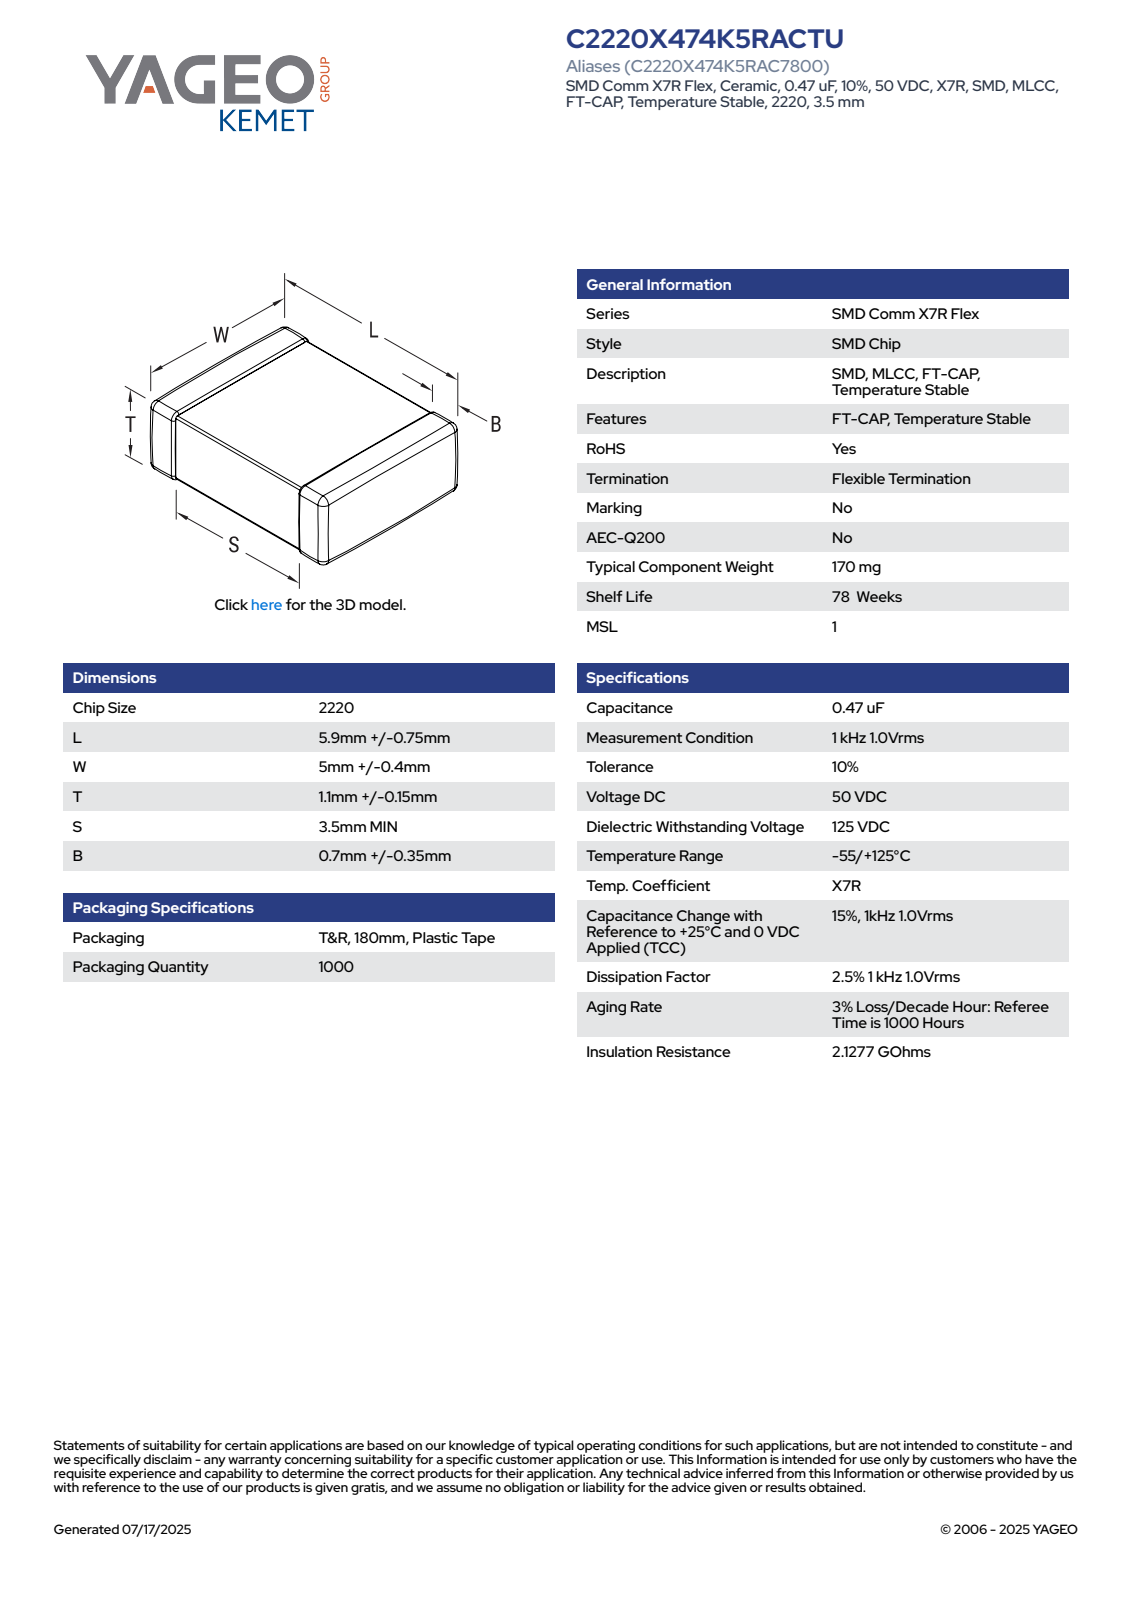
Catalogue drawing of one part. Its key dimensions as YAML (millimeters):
part_name: "CCS_CCSTDNOS_2220_L6.65W5.4T1.25B1.05"
step_written_by: "SolidWorks 2014 (AUTOMOTIVE_DESIGN)"
units: millimeters
bodies: {solids: 4, faces: 121, planar: 71, cylindrical: 34, other: 16}
overall_size: [6.65, 5.4, 1.25]
volume: 38
surface_area: 98
partial_cylinders:
  - {radius: 0.11, count: 24}
face_to_face_distances: [1.03, 1.14, 1.25, 6.65, 5.18, 5.29, 5.4, 2.51, 2.78, 2.62]
